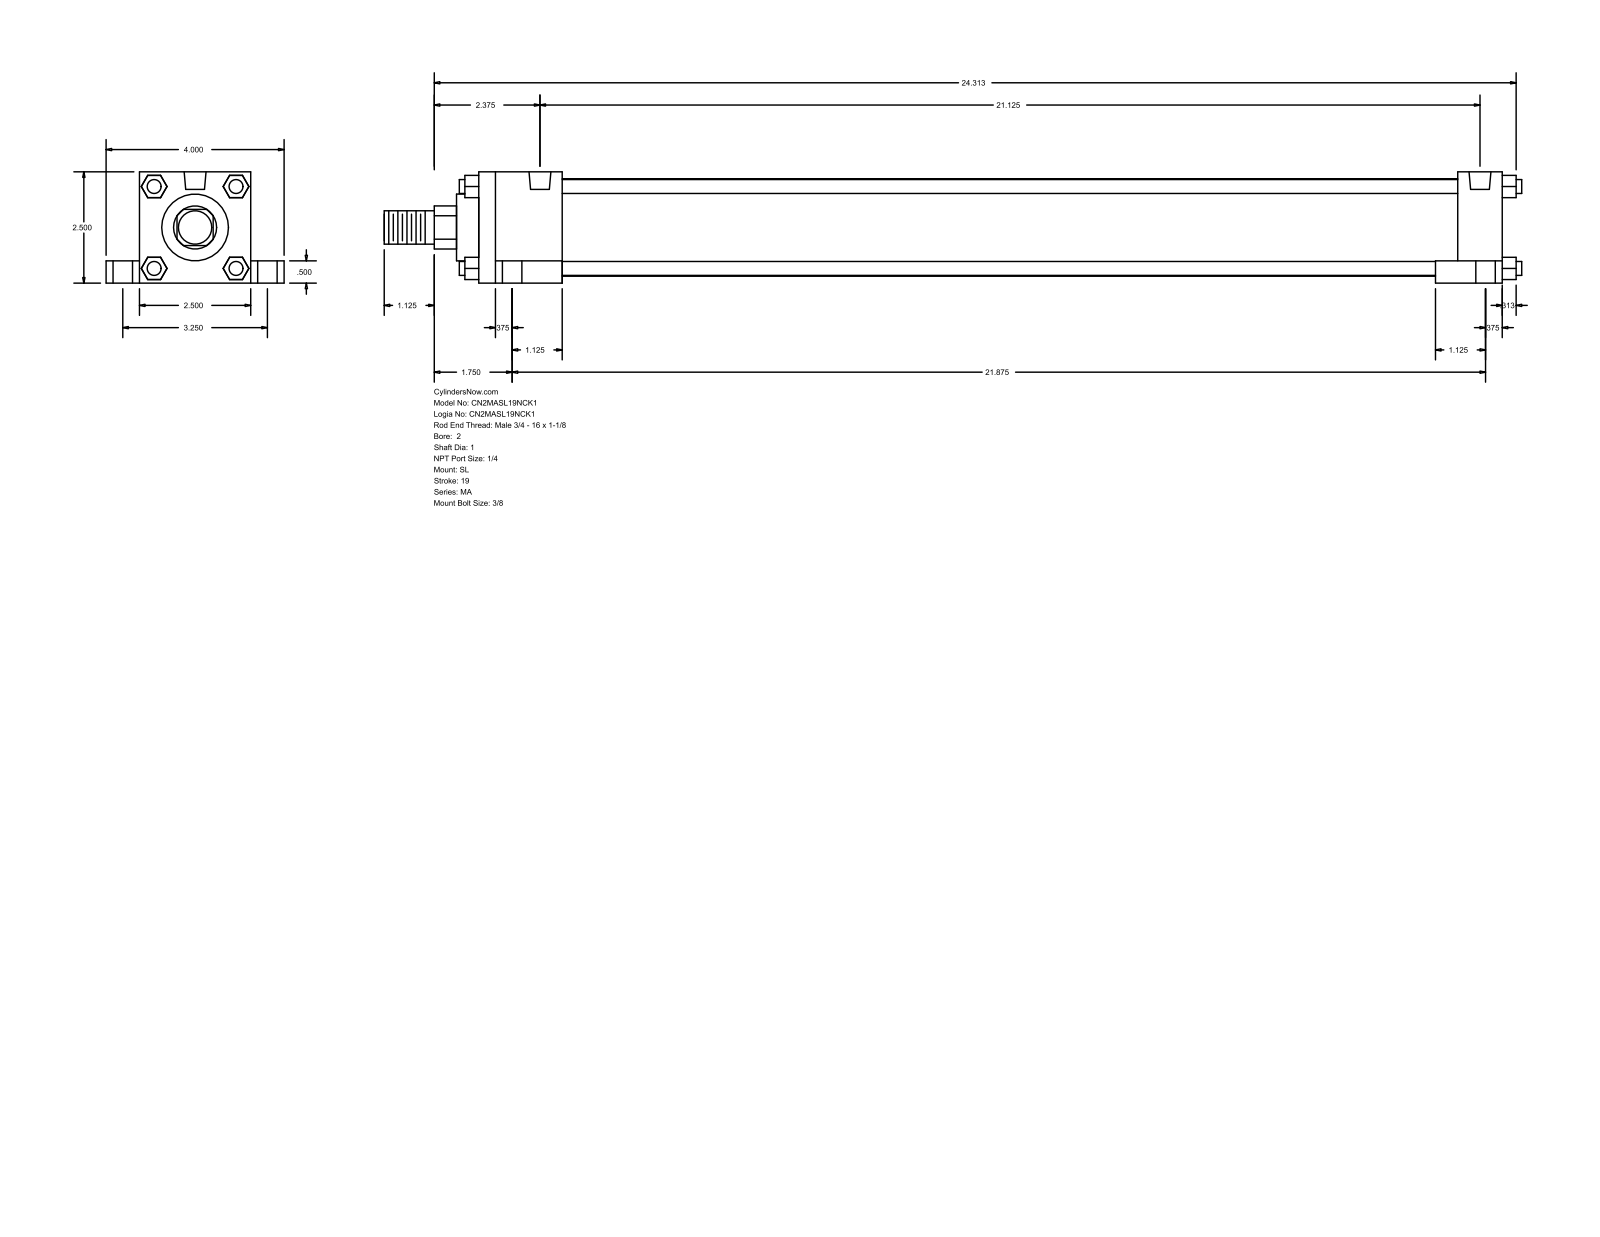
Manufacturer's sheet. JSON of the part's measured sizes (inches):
{"part_name": "MA_SL__0200_1", "step_written_by": "GSSL Pune (CONFIG_CONTROL_DESIGN)", "units": "inches", "bodies": {"solids": 0, "faces": 148, "planar": 112, "cylindrical": 36, "other": 0}, "overall_size": [25.563, 4, 2.5], "round_holes": [[0.313, 4], [0.437, 4], [0.687, 4], [0.492, 2]], "round_bosses_or_shafts": [[0.313, 4], [2.19, 1], [1.5, 1], [1, 1], [0.75, 1]], "partial_cylinders_radius": [[0.484, 1]], "face_to_face_distances": [2.5, 0.5, 23, 0.75, 3.25, 1, 2, 1.875, 21.125, 22], "hole_center_spacings": [1.63, 1.741, 3.25, 21.125, 21.312, 21.811, 21.875, 22.115]}
